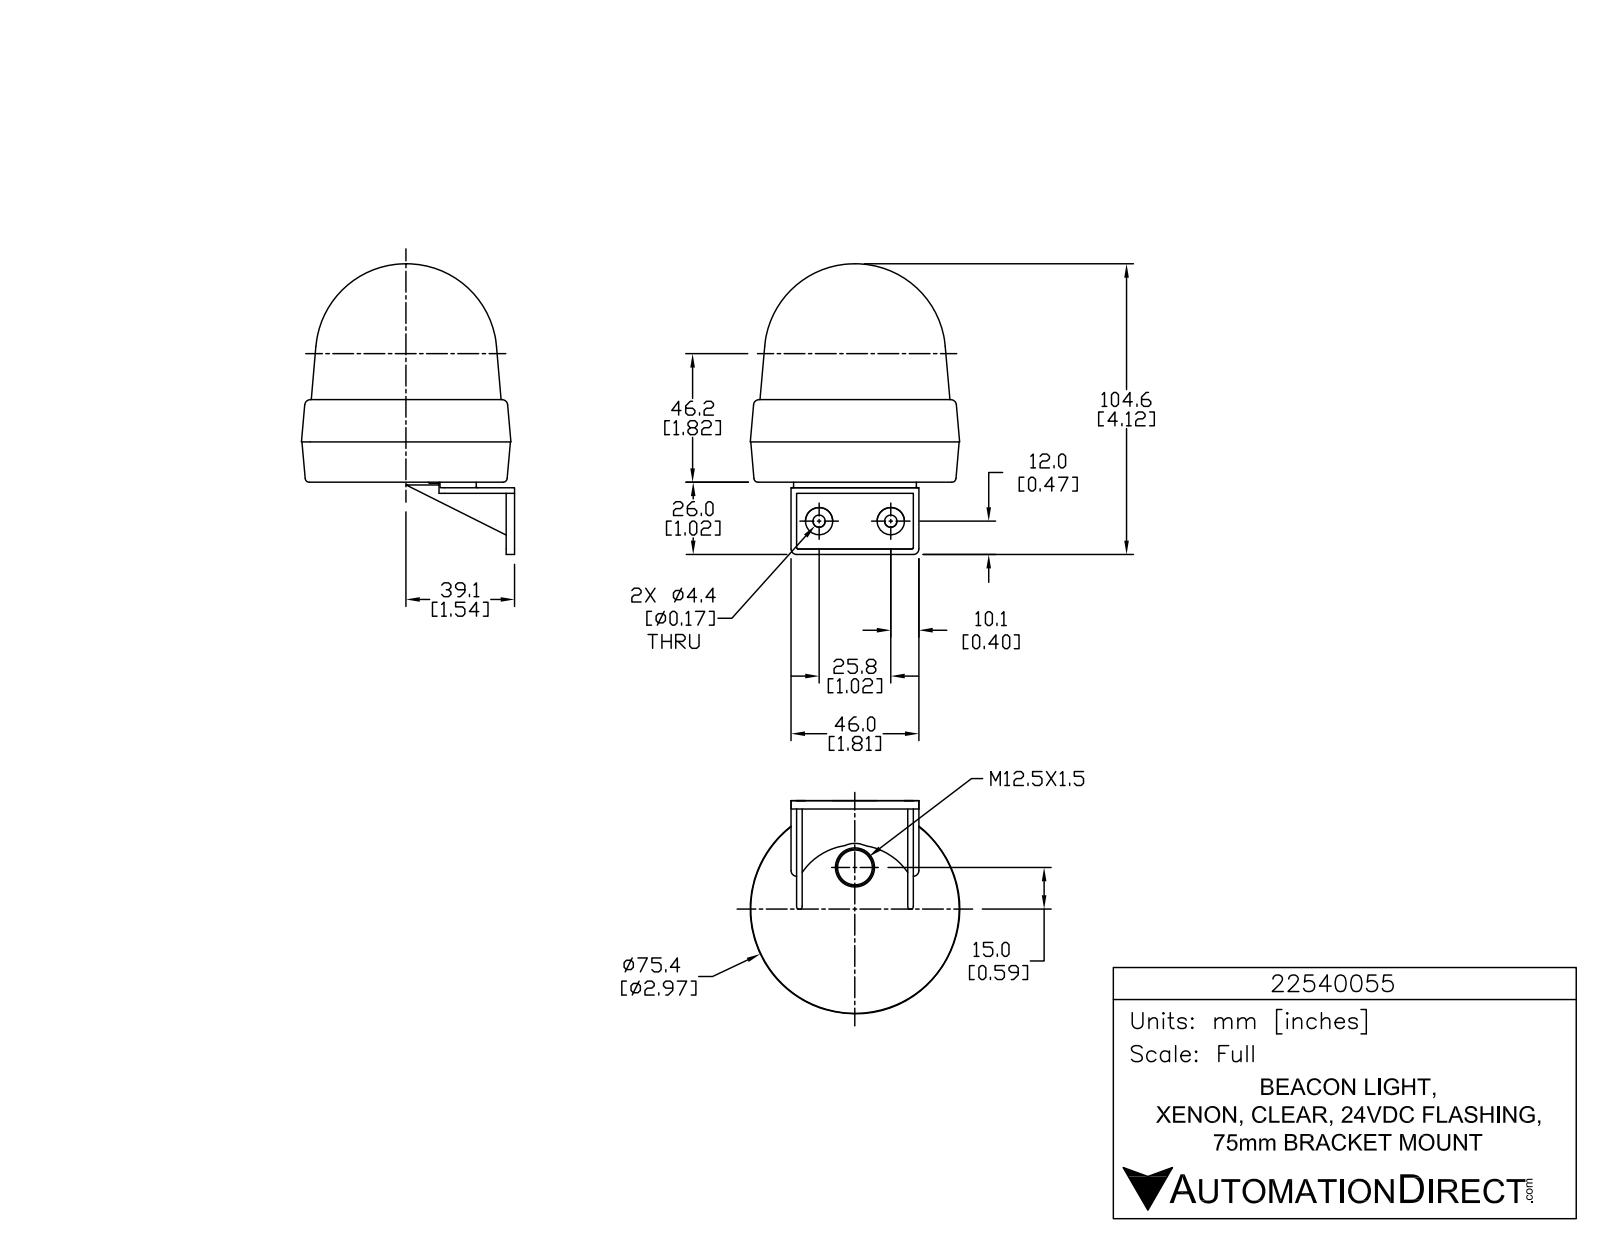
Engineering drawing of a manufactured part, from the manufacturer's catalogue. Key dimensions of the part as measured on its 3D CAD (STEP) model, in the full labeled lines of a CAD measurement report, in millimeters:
Part name (STEP PRODUCT): 22540055
STEP written by: SolidWorks 2015 (AUTOMOTIVE_DESIGN)
Units: millimetres
Bodies: 1 solid, 819 faces (549 planar, 180 cylindrical, 90 other)
Overall size (bounding box): 104.6 × 82.6 × 75.4
Volume: 262 500 mm³ · Surface area: 27 080 mm²
Round holes (diameter × count): ⌀1.5 ×3, ⌀4.4 ×2
Round bosses / shafts (diameter × count): ⌀8.6 ×3, ⌀2.1 ×3, ⌀9.8 ×2
Partial cylindrical surfaces — rounded edges, fillets, slot ends (radius × count): R0.1 ×9, R0.1 ×6, R0.3 ×6, R0.3 ×6, R0.3 ×6, R0.5 ×6, R5 ×6, R2 ×4
Main face-to-face distances: 2, 4, 40, 1, 3, 42, 38, 2, 42, 44
Hole centre spacings: 25.8
